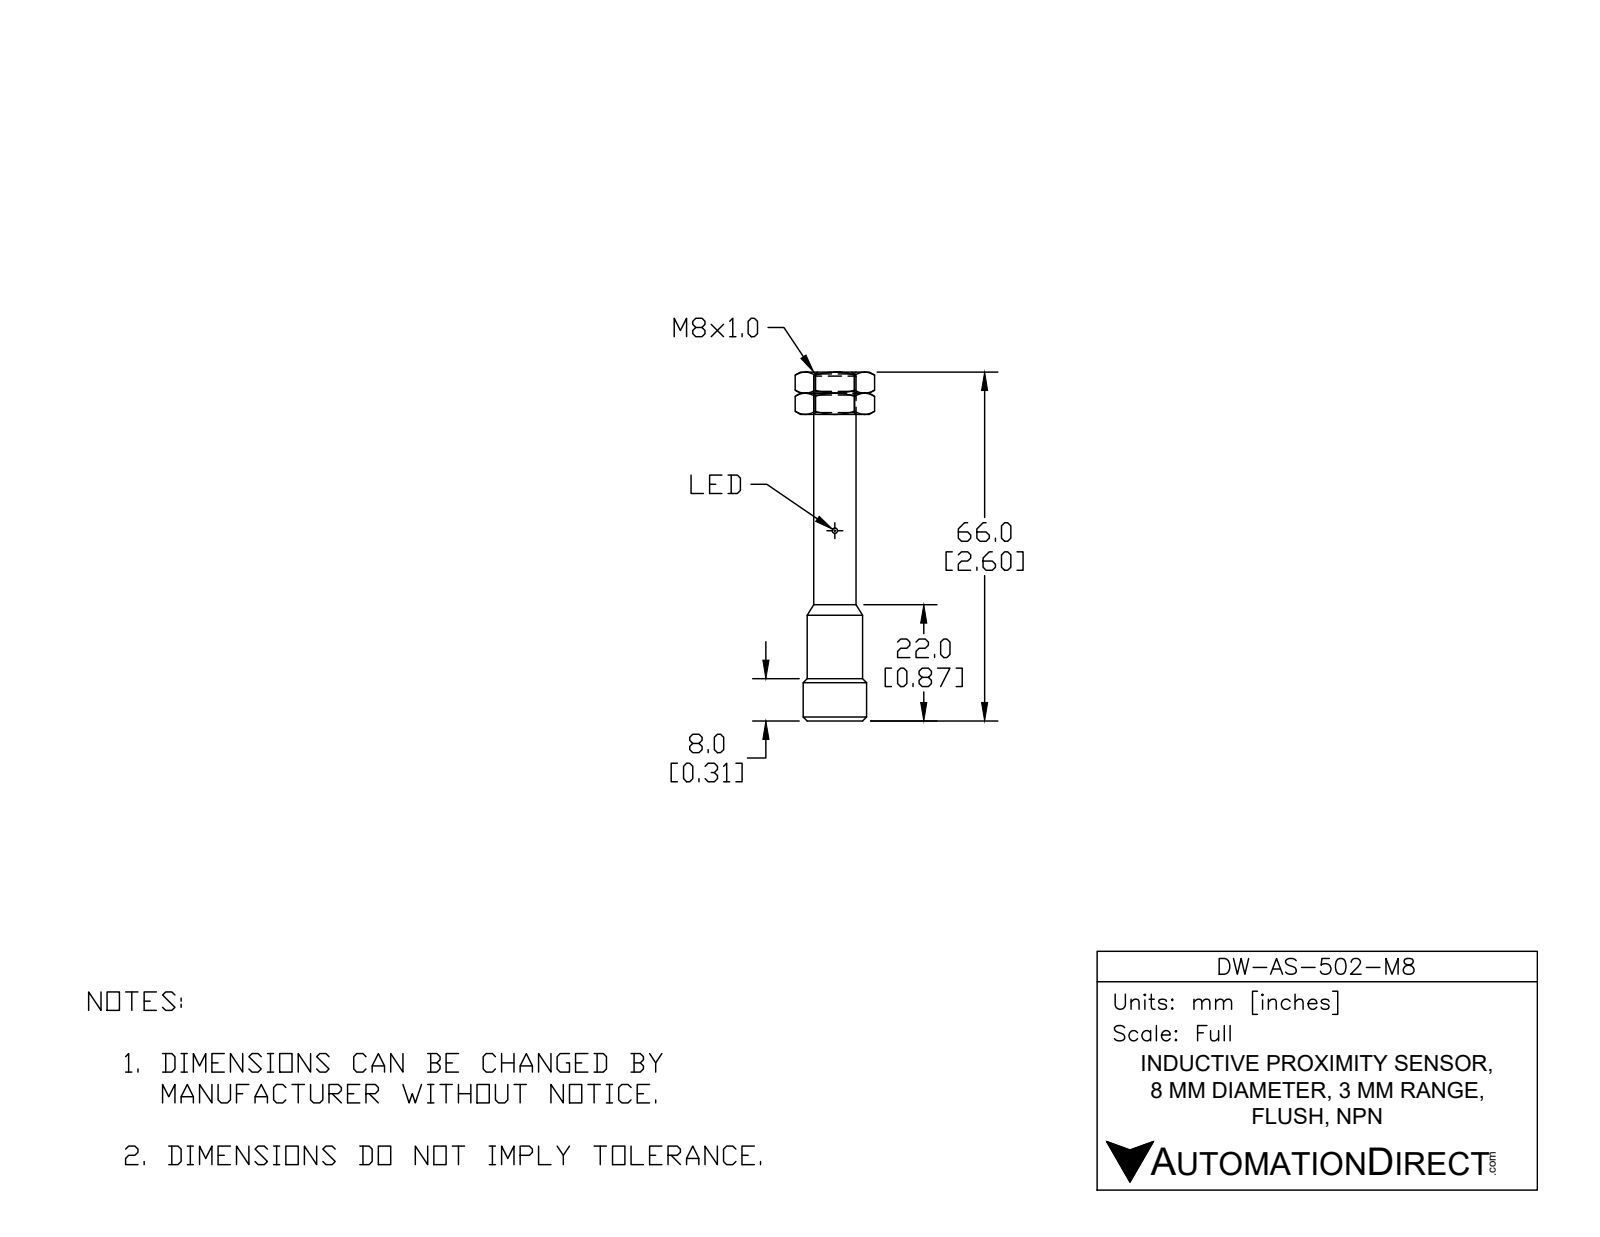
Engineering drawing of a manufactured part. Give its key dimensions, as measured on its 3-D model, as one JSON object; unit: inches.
{"part_name": "DW-AS-502-M8", "step_written_by": "SolidWorks 2017 (AUTOMOTIVE_DESIGN)", "units": "inches", "bodies": {"solids": 1, "faces": 35, "planar": 10, "cylindrical": 17, "other": 8}, "overall_size": [2.598, 0.472, 0.472], "volume_in3": 0.23, "surface_area_in2": 3.709, "round_holes": [[0.12, 2]], "round_bosses_or_shafts": [[0.039, 4], [0.472, 1], [0.415, 1], [0.335, 1], [0.315, 1]], "face_to_face_distances": [2.256, 2.598, 0.343, 1.811, 0.445, 0.787, 1.593, 0.218, 0.663, 1.005]}
